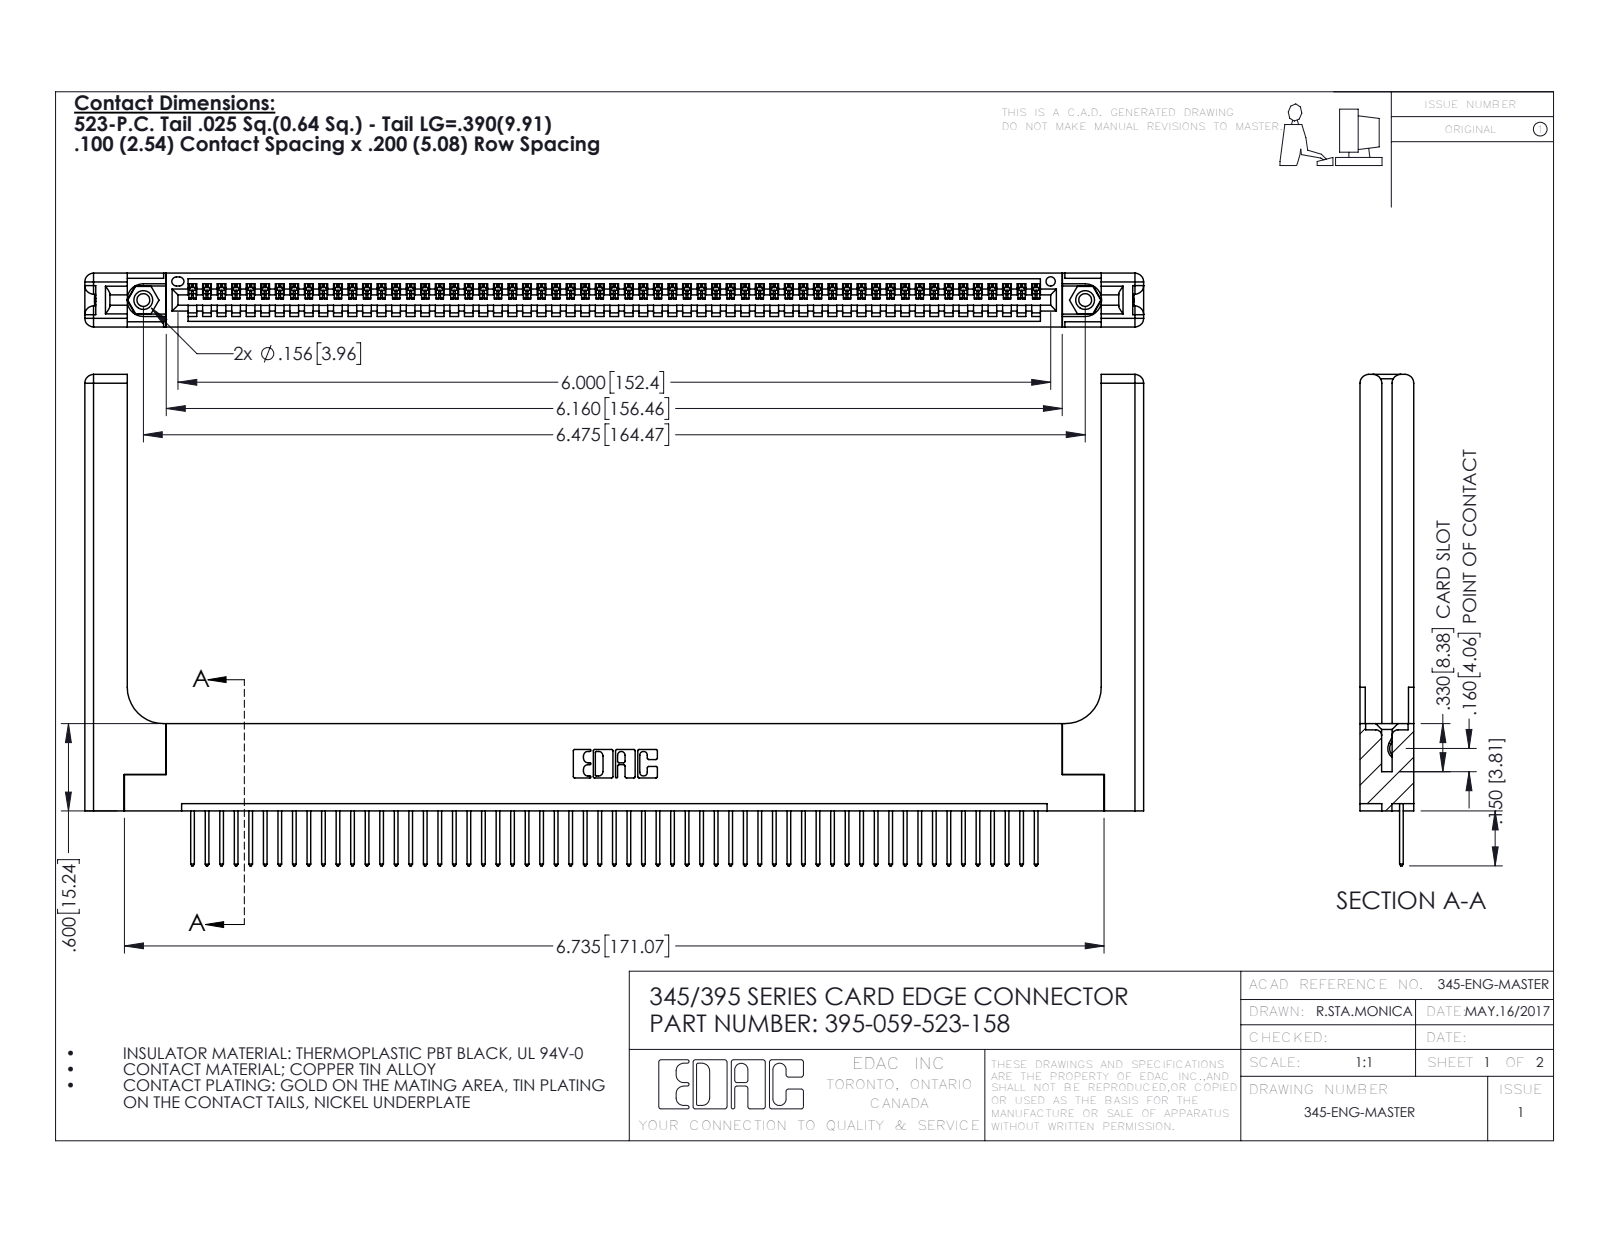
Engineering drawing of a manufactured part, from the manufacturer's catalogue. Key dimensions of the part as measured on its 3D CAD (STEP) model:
Part name (STEP PRODUCT): 345-250-001_345-250-001-102; 345 Part_Flush Mounting Lugs - 0.156 Dia-TH; 345-292-001_345-293-123; 345-220-058_345-220-058 (+1 more)
STEP written by: SolidWorks 2016 (CONFIG_CONTROL_DESIGN)
Units: inches
Bodies: 64 solids, 3804 faces (2588 planar, 1156 cylindrical, 60 other)
Overall size (bounding box): 7.279 × 3.377 × 0.37
Volume: 1.598 in³ · Surface area: 45.09 in²
Round holes (diameter × count): ⌀0.089 ×2, ⌀0.125 ×2, ⌀0.156 ×2, ⌀0.064 ×1
Round bosses / shafts (diameter × count): ⌀0.155 ×2
Partial cylindrical surfaces — rounded edges, fillets, slot ends (radius × count): R0.006 ×118, R0.01 ×118, R0.01 ×22, R0.06 ×16, R0.007 ×6, R0.031 ×6, R0.026 ×3, R0.03 ×2
Main face-to-face distances: 0.072, 0.298, 0.37, 0.2, 0.098, 0.272, 0.025, 0.225, 0.148, 0.15
Hole centre spacings: 0.27, 6.239, 6.475
